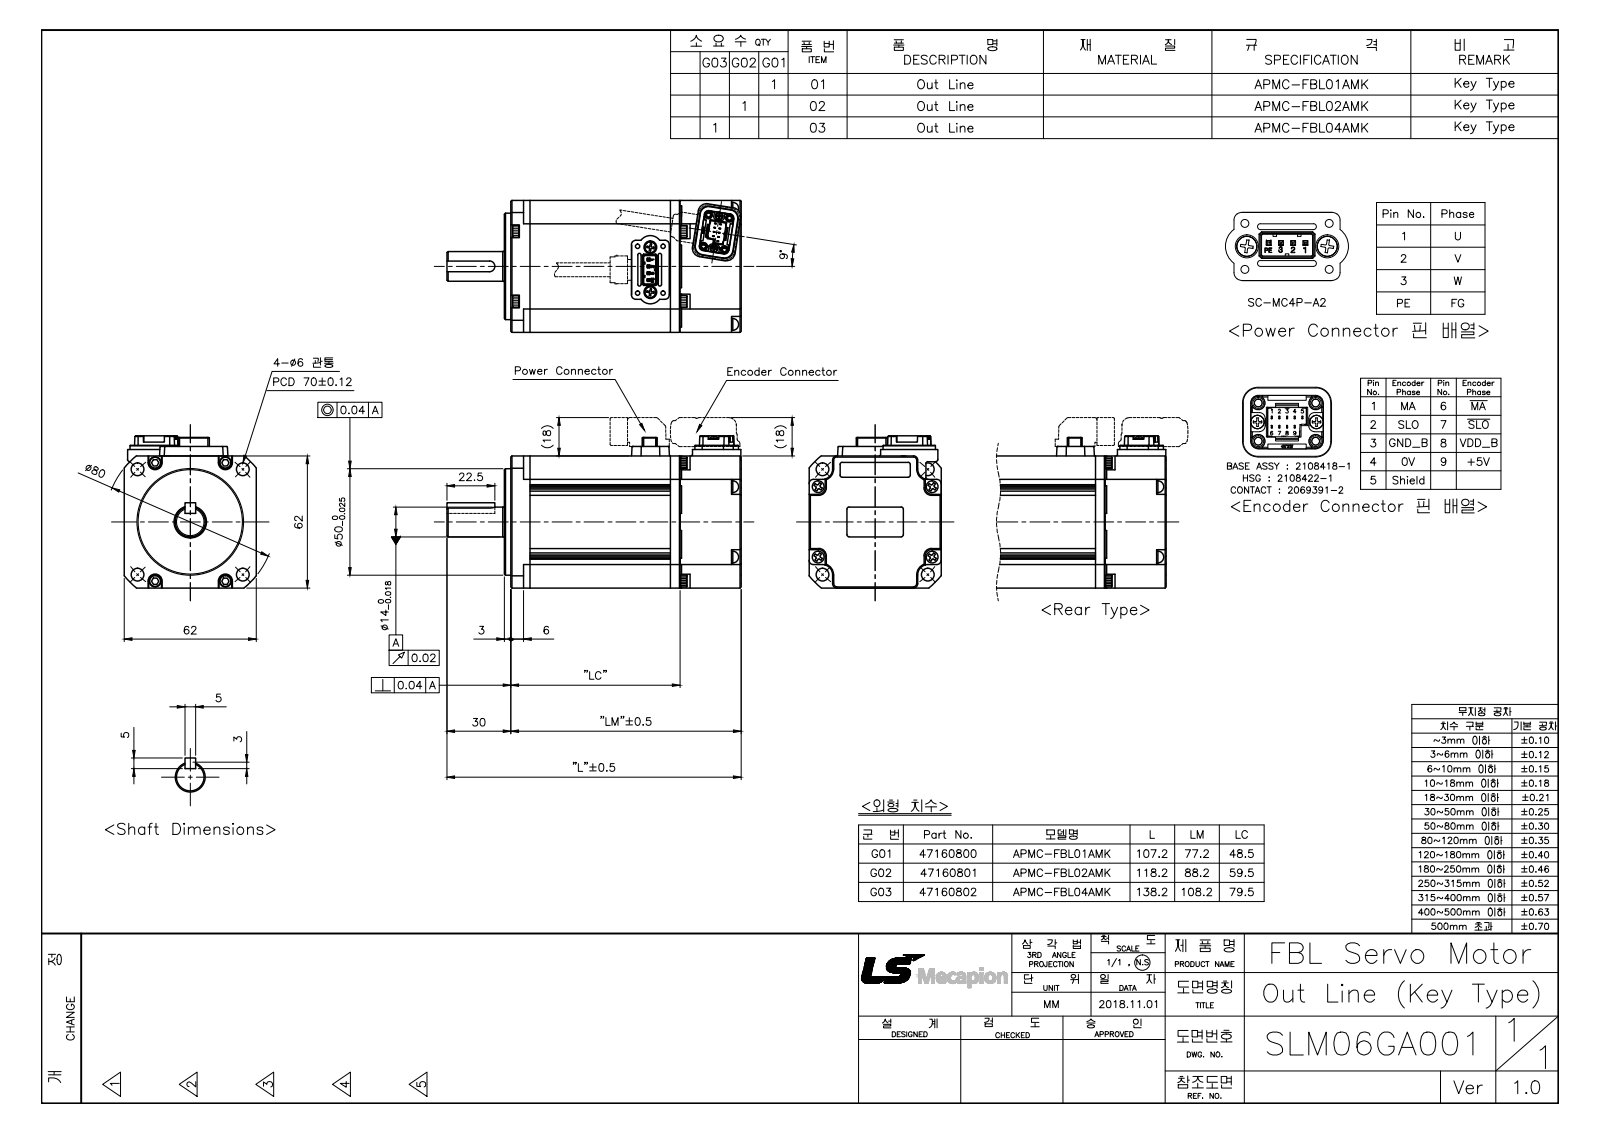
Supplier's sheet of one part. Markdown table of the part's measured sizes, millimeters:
| quantity | value |
| --- | --- |
| part name | SLM06GA001G02_Out Line(APMC-FBL02AMK) |
| STEP written by | SolidWorks 2011 (AUTOMOTIVE_DESIGN) |
| units | millimeters |
| bodies | 45 solids, 1820 faces (1162 planar, 469 cylindrical, 189 other) |
| overall size | 118.2 × 71.5 × 62 |
| volume | 312 728 mm³ |
| surface area | 71 053 mm² |
| round holes (diameter × count) | 2.1 × 10, 3 × 10, 3.5 × 8, 6 × 6, 3.1 × 4, 2 × 2, 3.3 × 1, 3.4 × 1, 15.3 × 1 |
| round bosses / shafts (diameter × count) | 5.4 × 6, 5.6 × 4, 5.5 × 4, 2.2 × 2, 50 × 1, 15 × 1, 14.8 × 1, 14 × 1 |
| partial cylindrical surfaces (radius × count) | 0.2 × 20, 0.3 × 20, 1 × 12, 0.15 × 9, 2 × 8, 3 × 8, 0.45 × 7, 0.11 × 6 |
| main face-to-face distances | 4.5, 0.7, 46, 50.5, 5.2, 51.2, 62, 3, 11, 28.7 |
| hole center spacings | 44.75, 6.02, 8.5, 8.8, 15.29, 16.01, 22.32, 31.47 |
